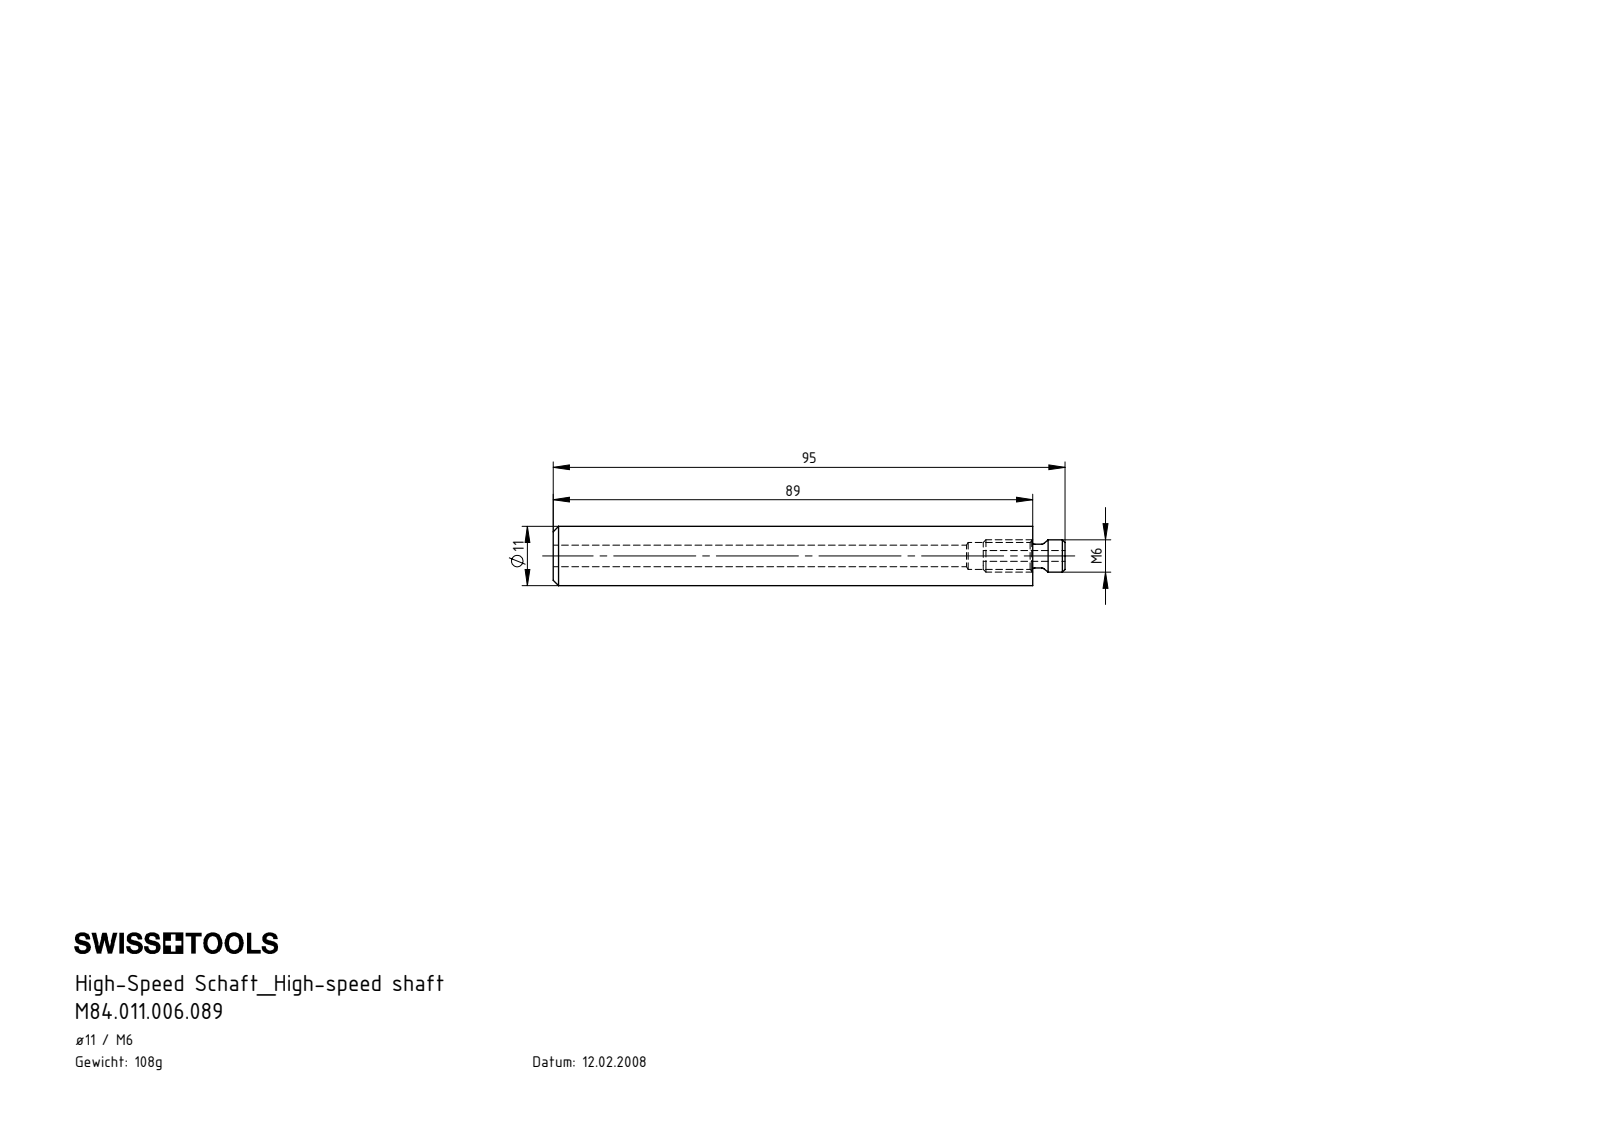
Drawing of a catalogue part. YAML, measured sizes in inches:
part_name: "U11.HS6.K01.089; HM1-BG1.006.015_A; HM1-U11.001.089_A"
step_written_by: "SolidWorks 2017 (AUTOMOTIVE_DESIGN)"
units: inches
bodies: {solids: 2, faces: 20, planar: 5, cylindrical: 7, other: 8}
overall_size: [3.74, 0.433, 0.433]
volume: 0.463
surface_area: 7.425
round_holes:
  - {diameter: 0.079, count: 1}
  - {diameter: 0.157, count: 1}
  - {diameter: 0.197, count: 1}
round_bosses_or_shafts:
  - {diameter: 0.433, count: 1}
  - {diameter: 0.236, count: 1}
  - {diameter: 0.173, count: 1}
face_to_face_distances: [3.504, 3.142, 3.74, 0.362, 0.598, 0.236, 3.496, 0.354, 0.244]
